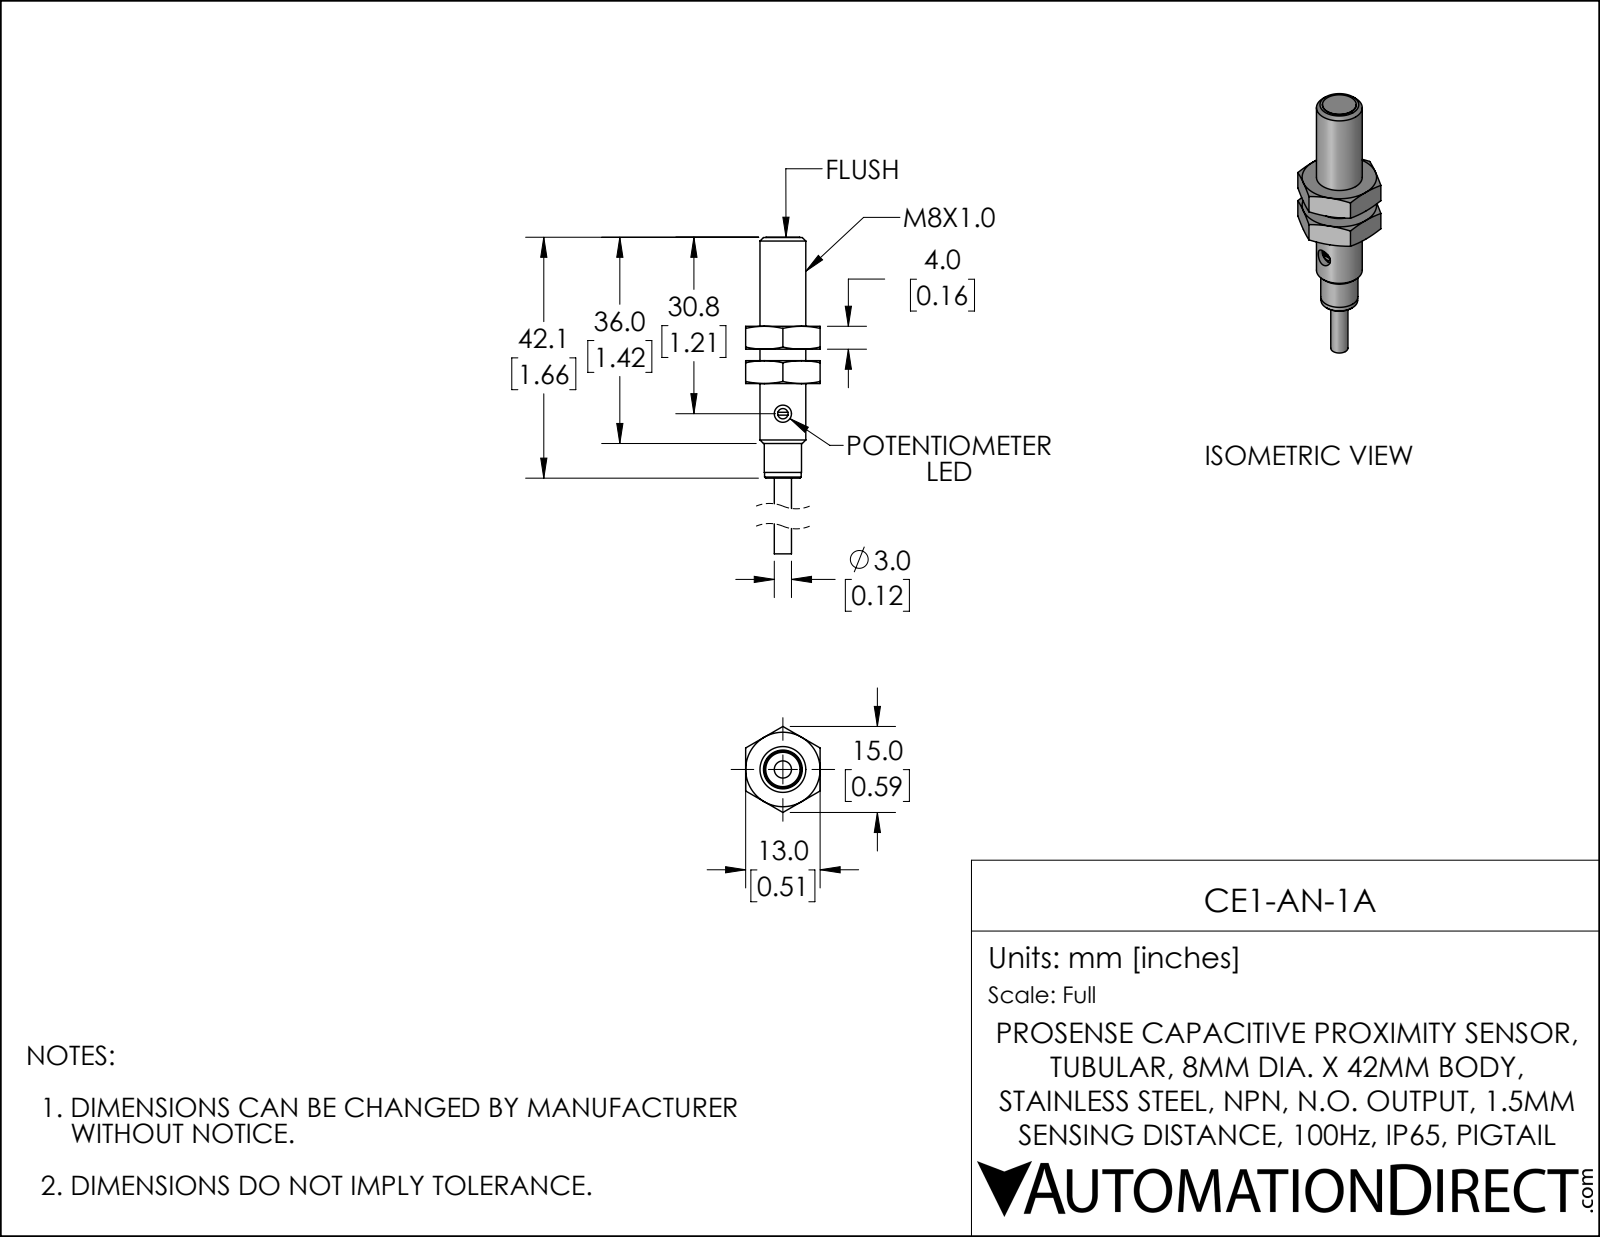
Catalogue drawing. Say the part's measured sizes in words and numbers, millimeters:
The part is named "CE1-AN-1A". Its 3-D file was written by "SolidWorks 2019 (CONFIG_CONTROL_DESIGN)". It is 3 solids with 68 faces: 28 planar, 9 cylindrical and 31 other. Overall it measures 52 by 15 by 13 millimeters. Its volume is 2 920 cubic millimeters and its surface area 2 137 square millimeters. Round holes: 1 of diameter 3, 1 of diameter 6.9. Round bosses or shafts: 1 of diameter 8, 1 of diameter 6.5, 1 of diameter 6.4, 1 of diameter 5.9, 1 of diameter 3, 1 of diameter 1.8. The main face-to-face distances are 13, 6, 4, 10, 2, 26.5, 15.5, 19.5, 21.5, 25.6.
